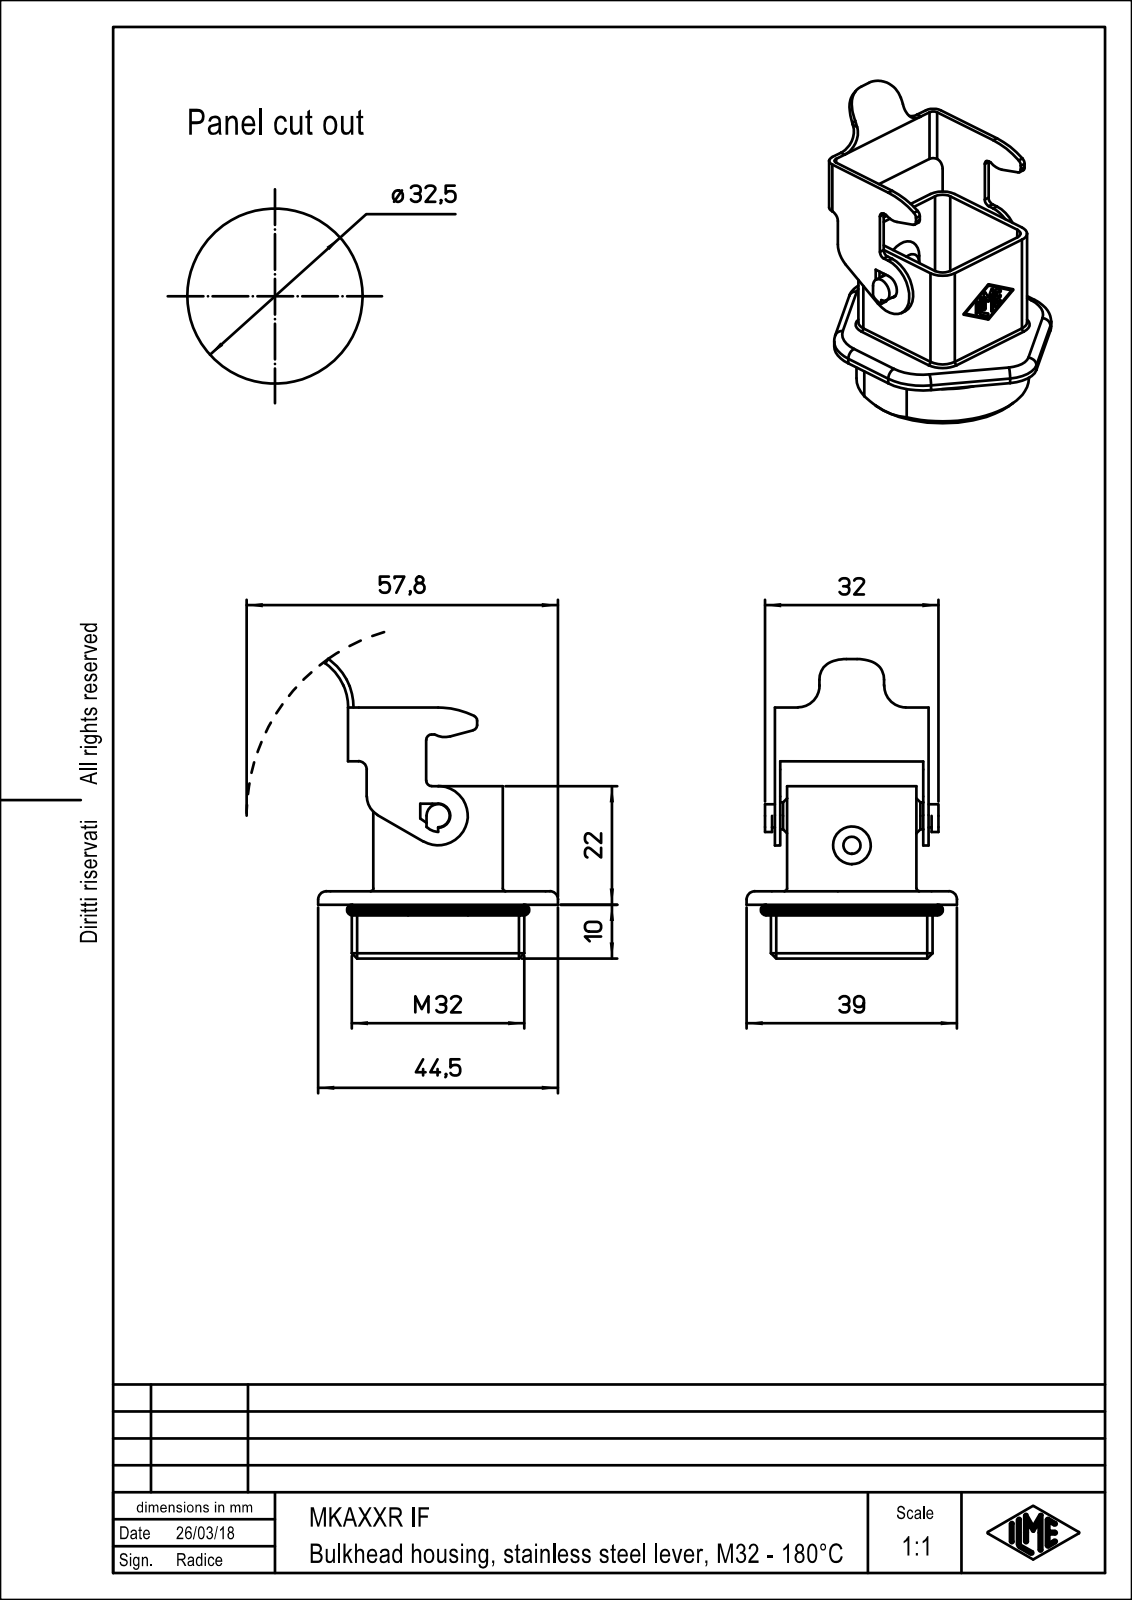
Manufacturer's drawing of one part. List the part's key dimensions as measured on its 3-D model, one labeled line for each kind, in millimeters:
Part name (STEP PRODUCT): MKAXXR_IF
STEP written by: PTC Creo Elements/Direct Modeling 19.0E 27-Jun-2016 (C) Parametric Technology GmbH (AUTOMOTIVE_DESIGN)
Units: millimetres
Bodies: 1 solid, 169 faces (75 planar, 72 cylindrical, 22 other)
Overall size (bounding box): 55.6 × 44.5 × 39
Volume: 9 261 mm³ · Surface area: 10 675 mm²
Round holes (diameter × count): ⌀3.2 ×1, ⌀7 ×1
Round bosses / shafts (diameter × count): ⌀29.8 ×1, ⌀5 ×1, ⌀4.3 ×1
Partial cylindrical surfaces — rounded edges, fillets, slot ends (radius × count): R1.5 ×7, R1 ×6, R2 ×6, R0.5 ×4, R3.2 ×4, R4 ×4, R9 ×4, R5 ×2
Main face-to-face distances: 1, 27.5, 24, 1.25, 25.25, 2.25, 26.25, 2.5, 28.5, 26.5
